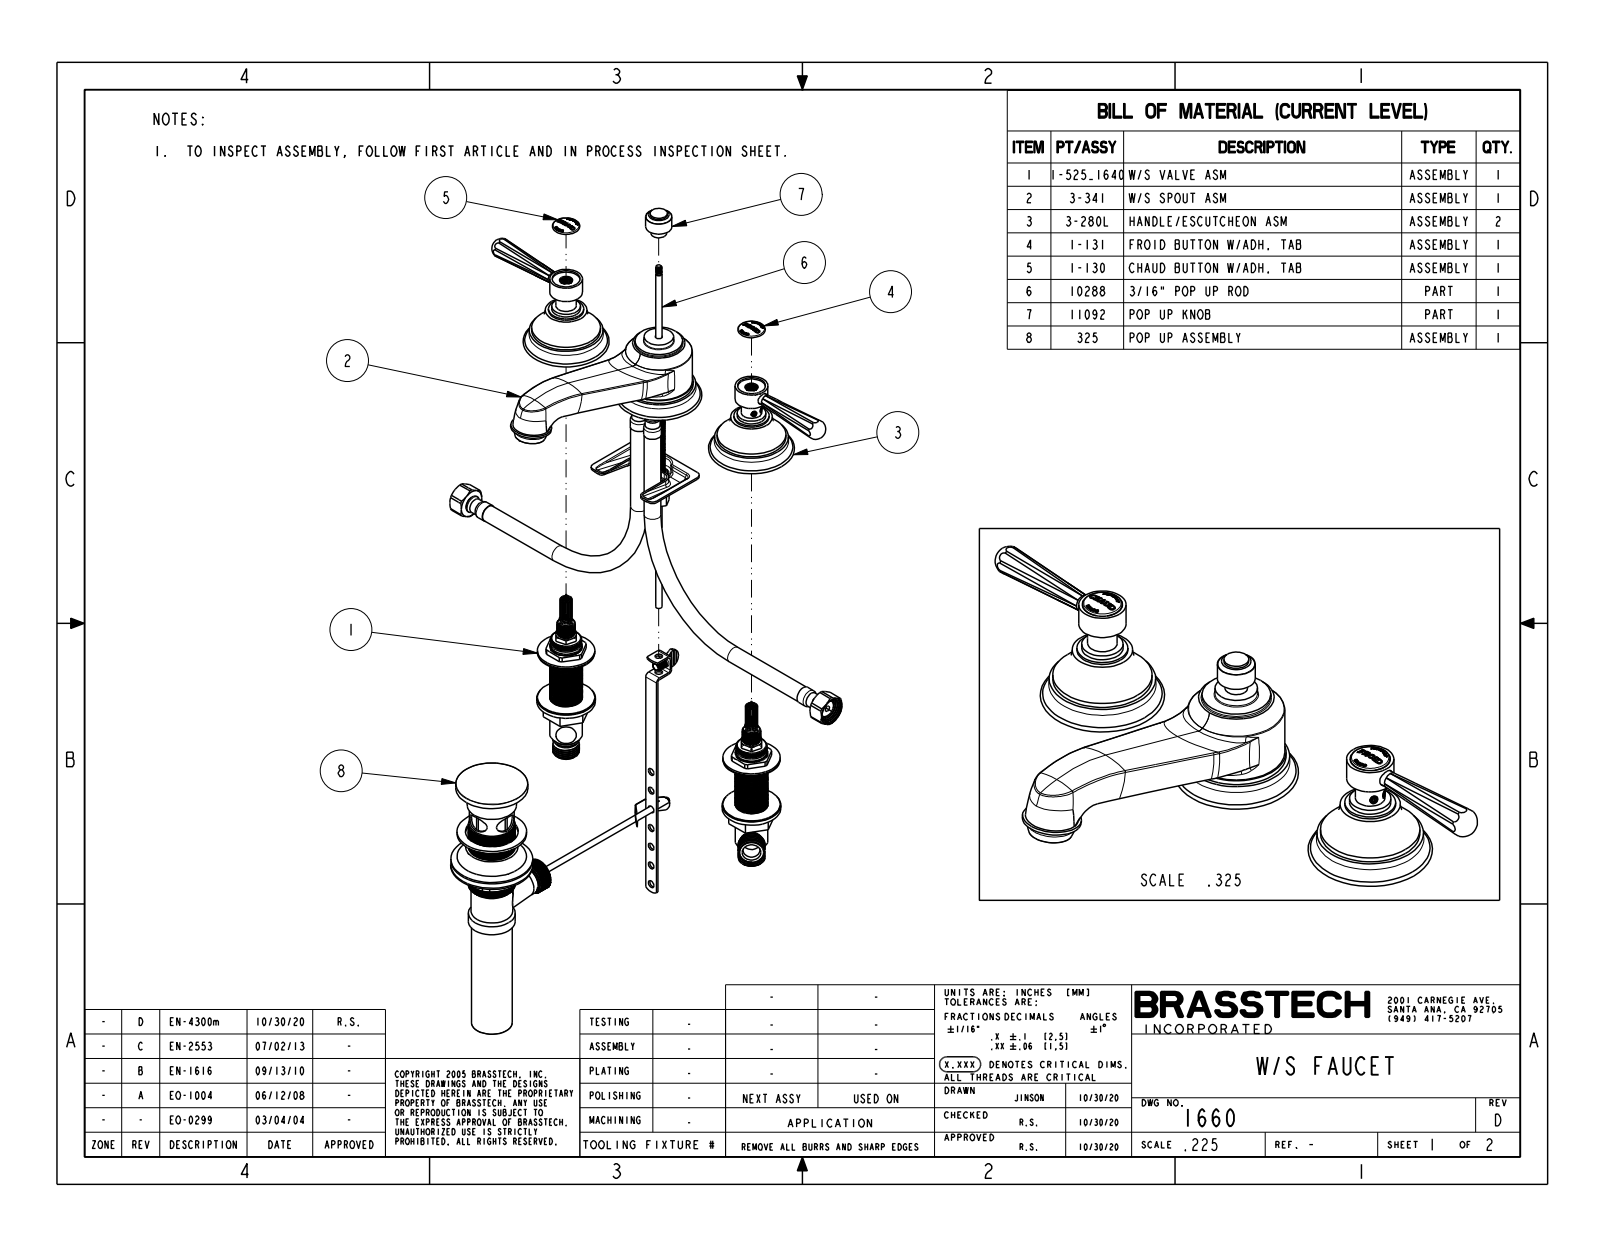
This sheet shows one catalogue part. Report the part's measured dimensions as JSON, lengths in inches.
{"part_name": "1660", "step_written_by": "CREO PARAMETRIC BY PTC INC, 2018400 (CONFIG_CONTROL_DESIGN)", "units": "inches", "bodies": {"solids": 3, "faces": 735, "planar": 319, "cylindrical": 213, "other": 203}, "overall_size": [14.149, 7.446, 2.982], "volume_in3": 22.88, "surface_area_in2": 94.67, "round_holes": [[0.85, 2]], "round_bosses_or_shafts": [[2.1, 3], [1, 3], [1.075, 2], [0.875, 2], [0.625, 2], [2.047, 1], [1.45, 1], [1.25, 1]], "partial_cylinders_radius": [[0.011, 20], [0.005, 10], [0.006, 10], [0.025, 9], [0.006, 8], [0.04, 8], [0.015, 6], [0.016, 5]], "face_to_face_distances": [0.475, 2.072, 1.597, 0.176, 0.175, 0.8, 0.1, 1.225, 0.75, 0.846], "hole_center_spacings": [8]}
